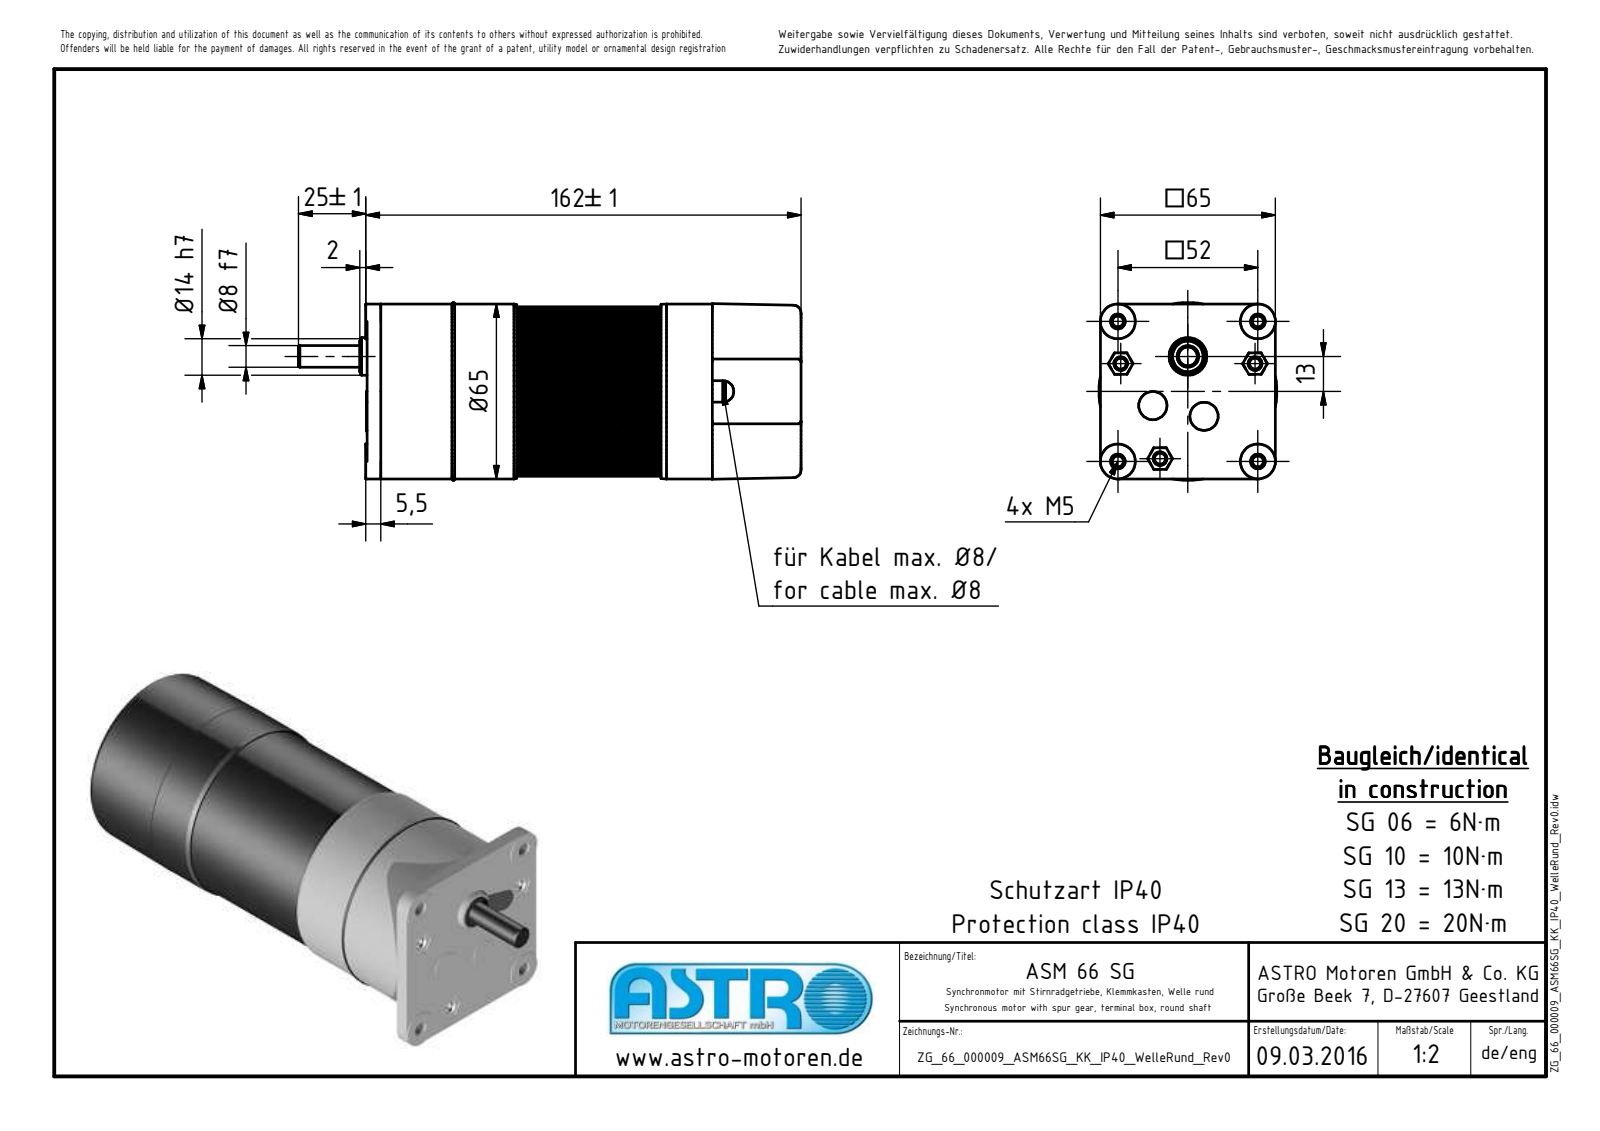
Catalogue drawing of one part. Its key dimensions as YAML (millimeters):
part_name: "ZG_66_000028_ASM66SG_KK_IP40_WelleRund_Rev0; 5101-STG-Kunst; LagerschaleB3-ZG-Rev1-0; ZG_51108x067_Endwelle_8x67_Rev0 (+6 more)"
step_written_by: "Autodesk Inventor 2010 (AUTOMOTIVE_DESIGN)"
units: millimeters
bodies: {solids: 14, faces: 456, planar: 183, cylindrical: 87, other: 186}
overall_size: [186.4, 65.38, 65.38]
volume: 296940
surface_area: 99551
round_holes:
  - {diameter: 4.1, count: 8}
  - {diameter: 5.2, count: 3}
  - {diameter: 4.3, count: 1}
  - {diameter: 6, count: 1}
  - {diameter: 8, count: 1}
  - {diameter: 8.5, count: 1}
  - {diameter: 12, count: 1}
  - {diameter: 15.5, count: 1}
  - {diameter: 16, count: 1}
  - {diameter: 59, count: 1}
  - {diameter: 63, count: 1}
round_bosses_or_shafts:
  - {diameter: 13, count: 4}
  - {diameter: 4, count: 4}
  - {diameter: 3.62, count: 4}
  - {diameter: 12.01, count: 2}
  - {diameter: 10.5, count: 2}
  - {diameter: 8.5, count: 2}
  - {diameter: 3, count: 2}
  - {diameter: 2.5, count: 2}
partial_cylinders:
  - {radius: 0.5, count: 16}
  - {radius: 1, count: 5}
  - {radius: 5.26, count: 4}
  - {radius: 4, count: 1}
face_to_face_distances: [44.8, 127.4, 104.1, 59.3, 7, 51.8, 111.1, 120.4, 75.6, 16.3]
hole_center_spacings: [27, 49.89, 20.66, 38.18, 44.9, 52.96, 10.53, 10.54]
